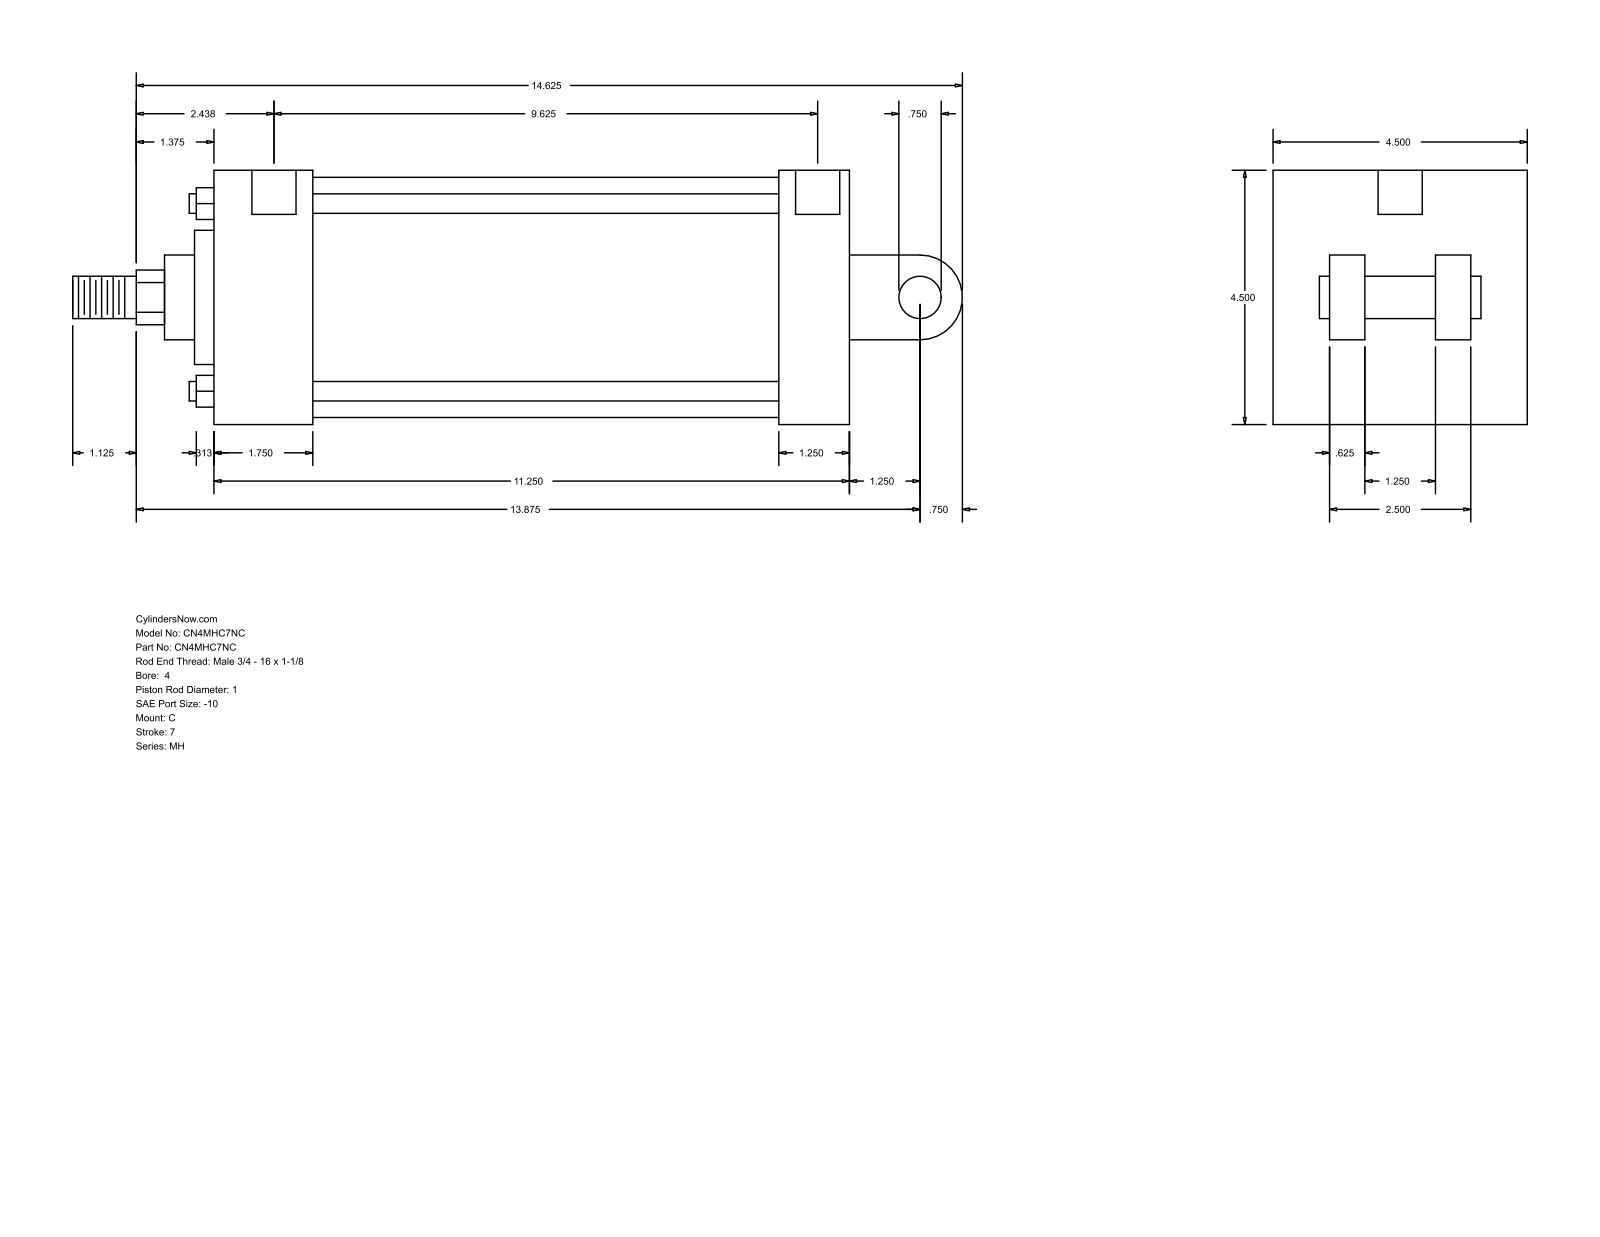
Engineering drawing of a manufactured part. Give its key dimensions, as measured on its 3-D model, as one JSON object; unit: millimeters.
{"part_name": "MH_C__0400_1", "step_written_by": "GSSL Pune (CONFIG_CONTROL_DESIGN)", "units": "millimeters", "bodies": {"solids": 0, "faces": 101, "planar": 71, "cylindrical": 30, "other": 0}, "overall_size": [400.05, 114.3, 114.3], "round_holes": [[8.73, 4], [19.84, 2]], "round_bosses_or_shafts": [[8.76, 4], [19.05, 2], [107.95, 1], [60.33, 1], [38.1, 1], [25.4, 1]], "partial_cylinders_radius": [[12.29, 1], [19.05, 1]], "face_to_face_distances": [114.3, 285.76, 44.46, 254.01, 209.55, 241.3, 31.75, 73.03, 41.27, 38.1], "hole_center_spacings": [247.65, 1.58, 1.59, 244.48, 246.06, 246.07]}
